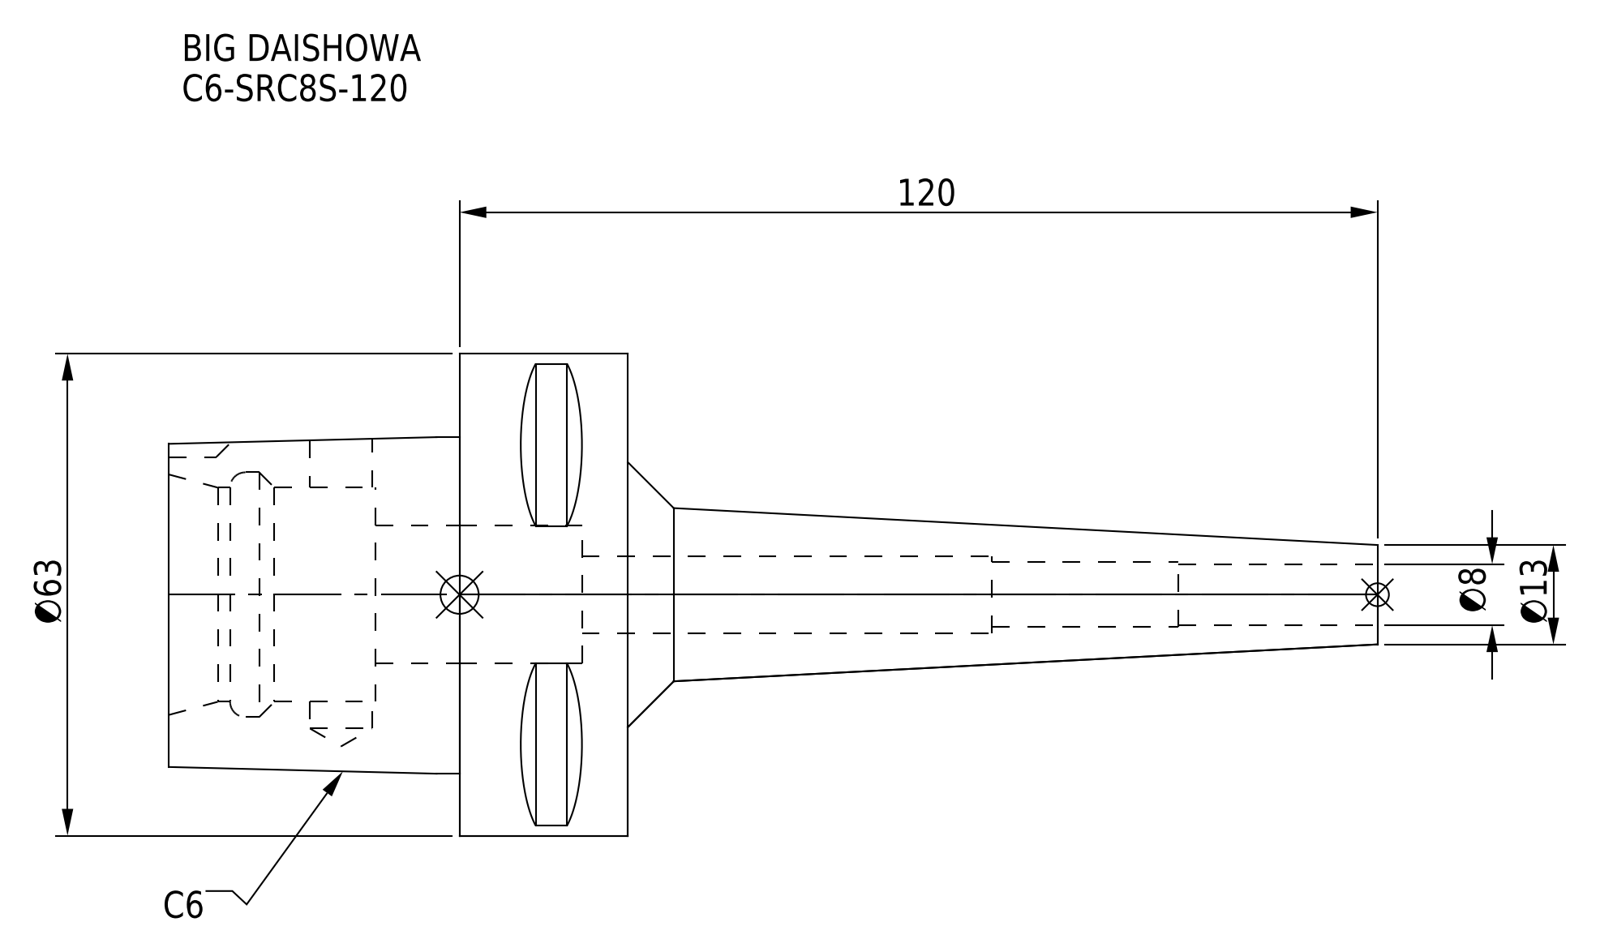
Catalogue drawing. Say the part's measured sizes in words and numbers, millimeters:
The part is named "C6-SRC8S-120". Its 3-D file was written by "CREO PARAMETRIC BY PTC INC, 2016380 (AUTOMOTIVE_DESIGN)". It is 1 solid with 65 faces: 30 planar, 21 cylindrical and 14 other. Overall it measures 158 by 63 by 63 millimeters. Its volume is 117 114 cubic millimeters and its surface area 28 149 square millimeters. Round holes: 1 of diameter 8, 1 of diameter 8.1, 1 of diameter 8.5, 1 of diameter 10, 1 of diameter 18, 1 of diameter 28, 1 of diameter 32. Round bosses or shafts: 1 of diameter 63. Partial cylindrical surfaces (rounded edges, fillets, slot ends): 1 of radius 5. The main face-to-face distances are 22, 27, 60, 38, 33, 11, 24.89, 55.4, 6, 16.
